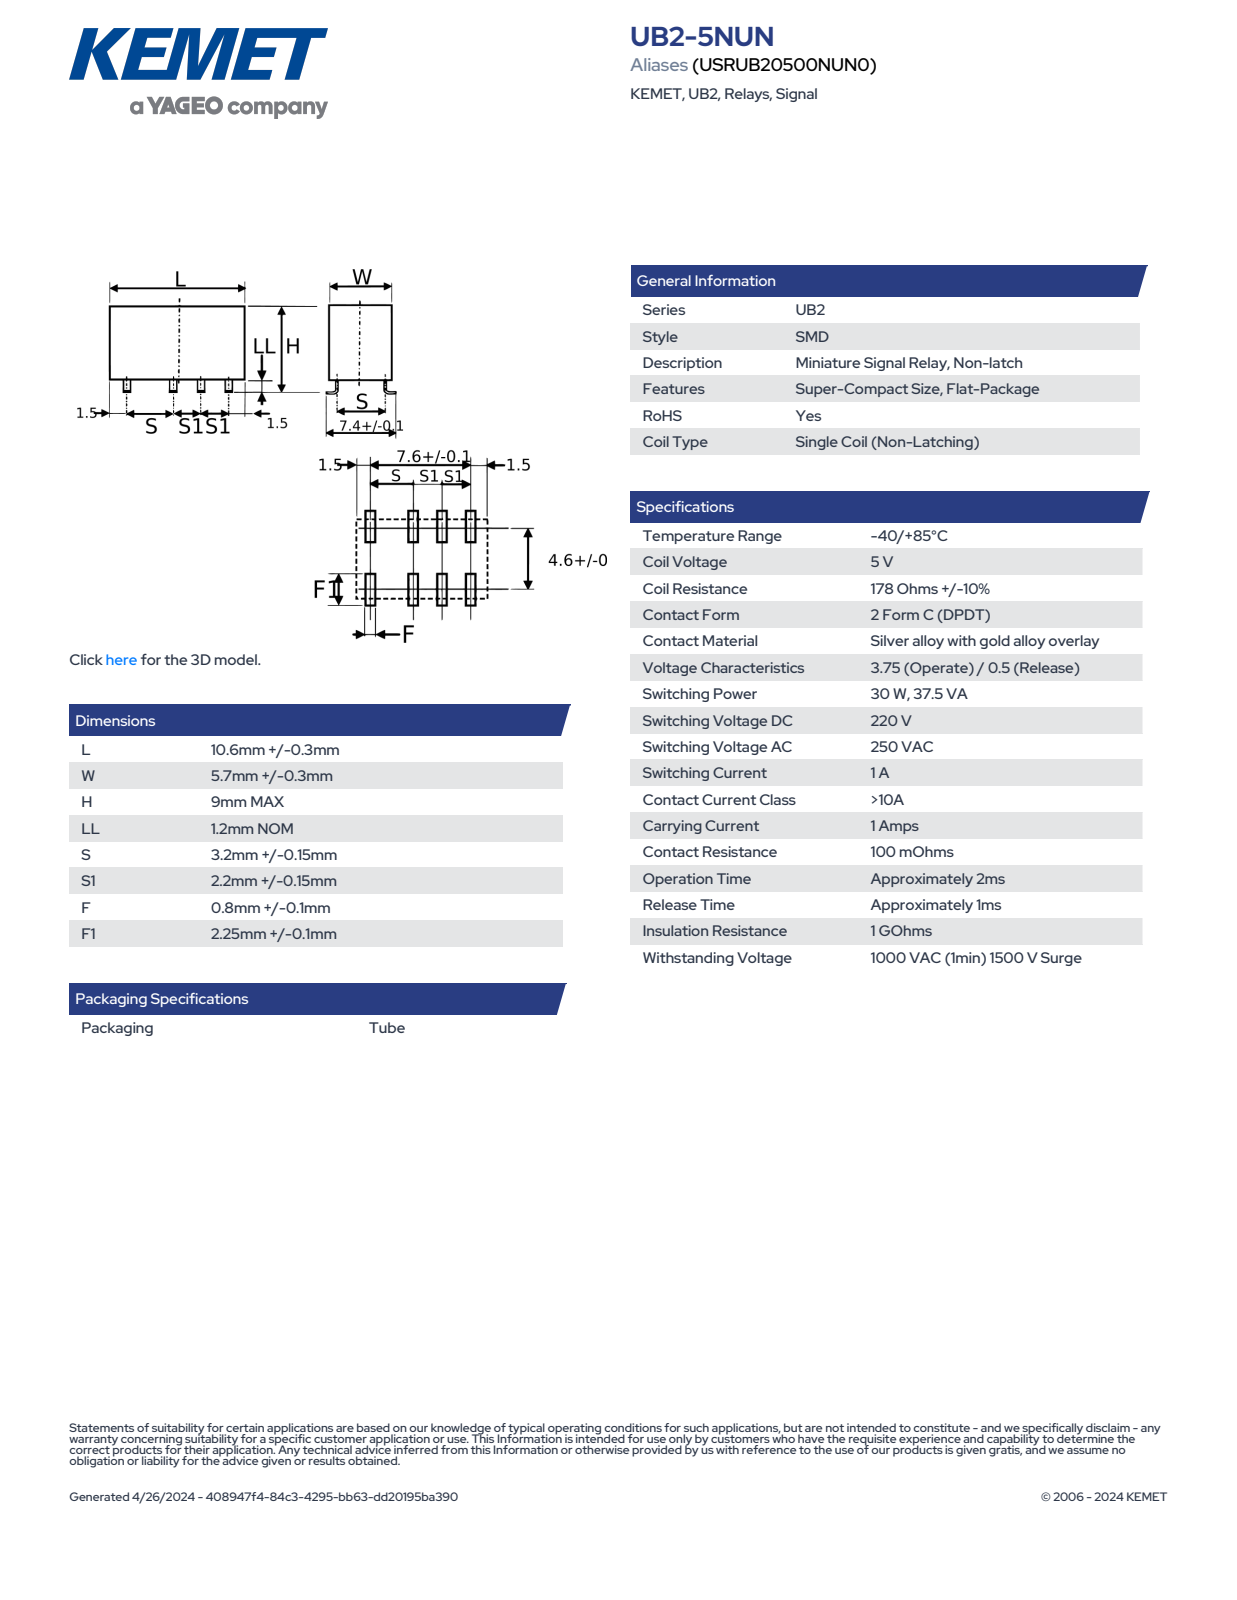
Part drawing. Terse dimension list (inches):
name: IR_TUB2M_L10.9W6H9
written by: SolidWorks 2014 (AUTOMOTIVE_DESIGN)
unit: in
bodies: 1 solid, 116 faces (116 planar, 0 cylindrical, 0 other)
size: 0.429 × 0.355 × 0.236
volume: 0.033 in³; area: 0.685 in²
face distances: 0.236, 0.327, 0.429, 0.028, 0.354, 0.024, 0.35, 0.179, 0.126, 0.057
